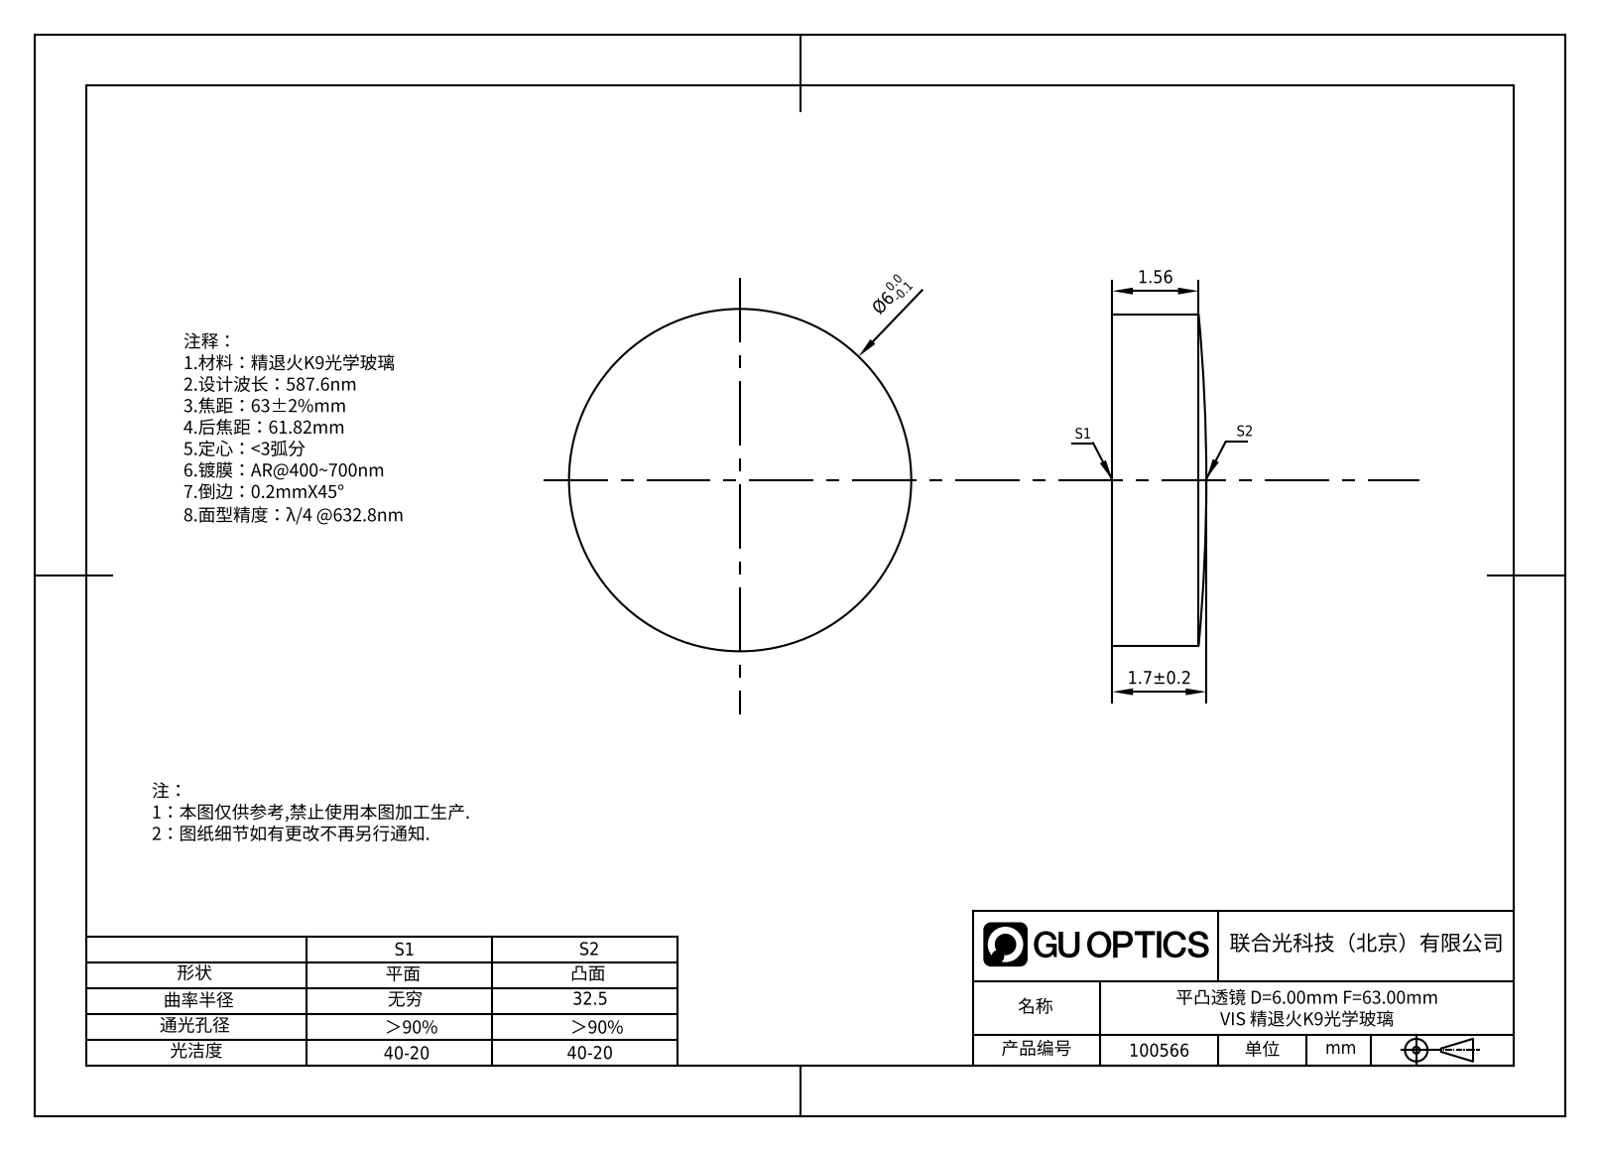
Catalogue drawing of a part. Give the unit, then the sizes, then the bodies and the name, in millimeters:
Units: millimetres
Overall size (bounding box): 6 × 6 × 1.7
Round bosses / shafts (diameter × count): ⌀6 ×1
Volume: 46 mm³ · Surface area: 86 mm²
Bodies: 1 solid, 5 faces (1 planar, 2 cylindrical, 2 other)
Part name (STEP PRODUCT): 100566
STEP written by: SolidWorks 2020 (CONFIG_CONTROL_DESIGN)
